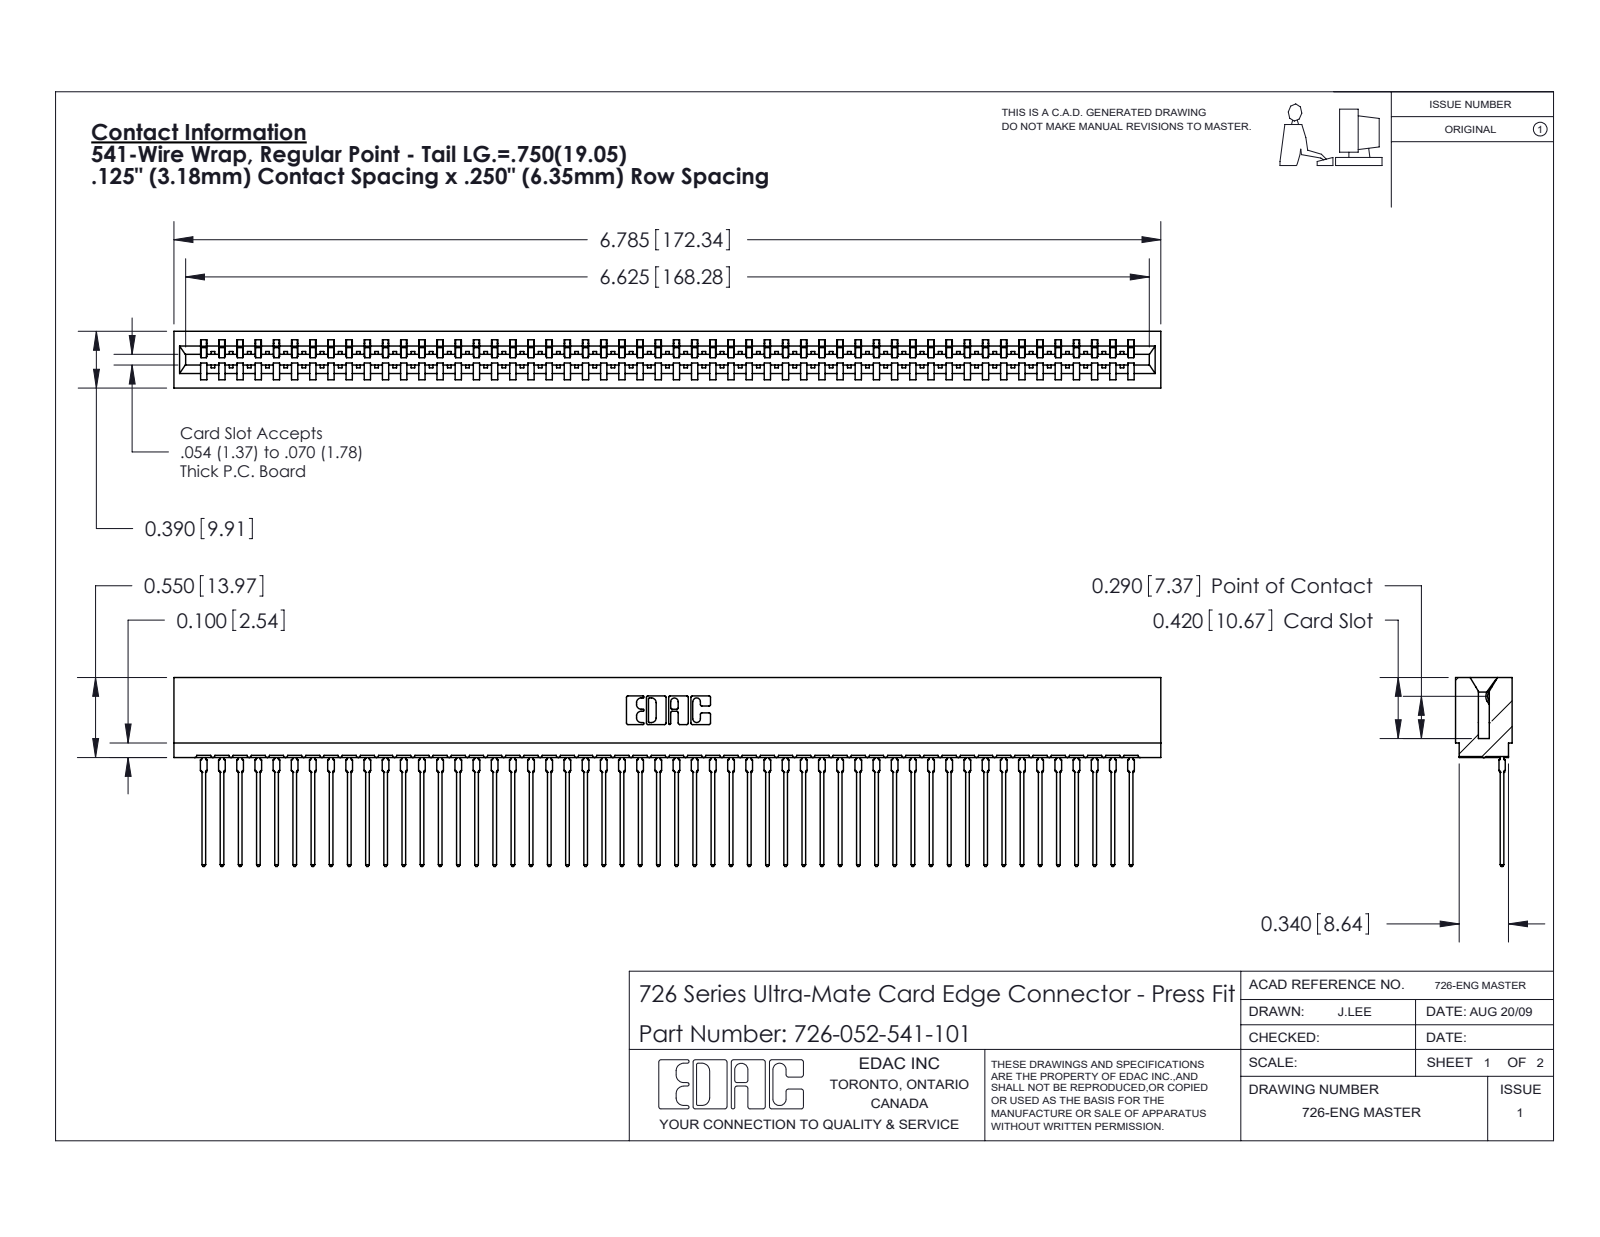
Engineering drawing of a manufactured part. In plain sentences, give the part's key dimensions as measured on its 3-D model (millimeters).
The part is named "746-292-001_541; 726-052-541-101; 726 Part_.515 Slot Depth - 01". Its 3-D file was written by "SolidWorks 2020 (CONFIG_CONTROL_DESIGN)". It is 53 solids with 5713 faces: 3331 planar, 1030 cylindrical and 1352 other. Overall it measures 172.3 by 33 by 9.9 millimeters. Its volume is 15 600 cubic millimeters and its surface area 25 170 square millimeters. Partial cylindrical surfaces (rounded edges, fillets, slot ends): 104 of radius 0.5, 53 of radius 0.4, 22 of radius 0.3, 6 of radius 0.2, 6 of radius 0.8, 4 of radius 0.1, 4 of radius 0.3, 3 of radius 0.7. The main face-to-face distances are 1.4, 8.5, 9.9, 0.6, 7.8, 6.4, 2.1, 7, 9.3, 0.8.
